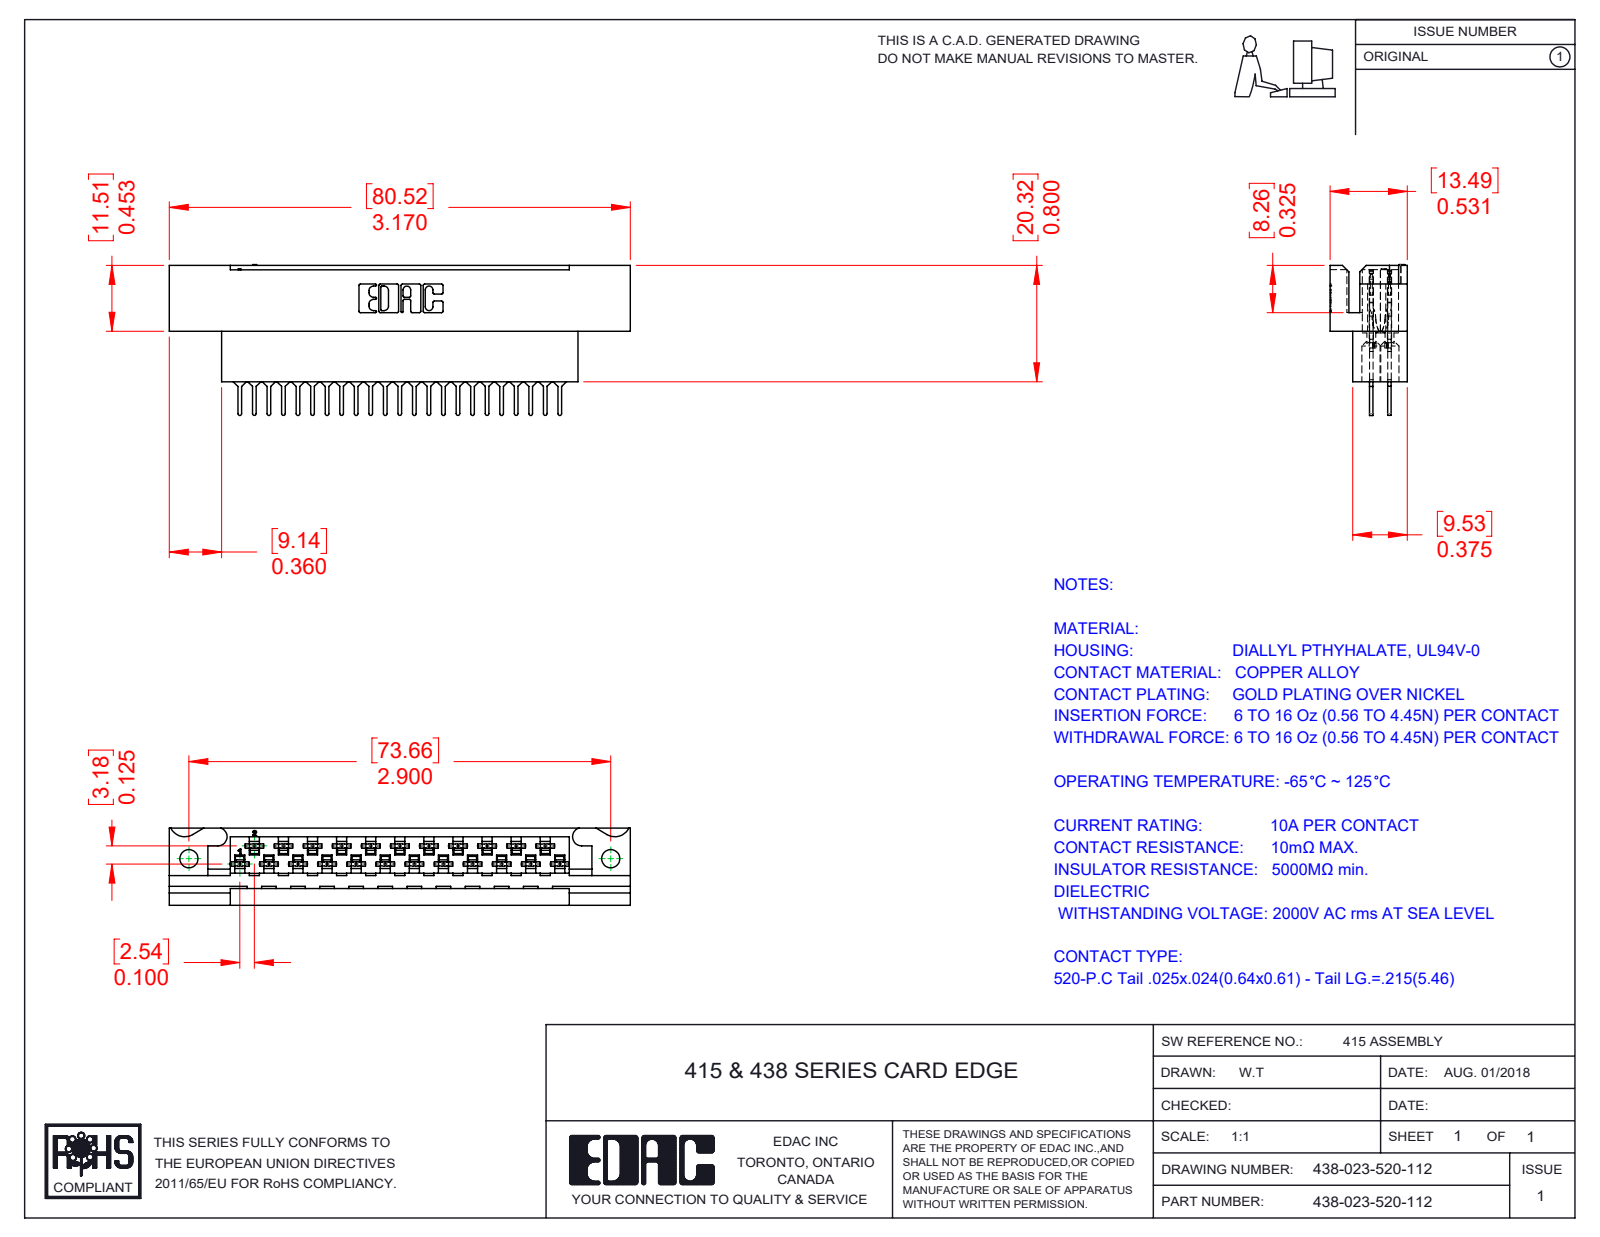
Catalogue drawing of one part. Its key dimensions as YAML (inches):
part_name: "438-210-001_438-210-023-112; 438-023-520-112; 516-290-001_520"
step_written_by: "SolidWorks 2016 (CONFIG_CONTROL_DESIGN)"
units: inches
bodies: {solids: 24, faces: 2410, planar: 1533, cylindrical: 648, other: 229}
overall_size: [3.17, 1.036, 0.531]
volume: 0.787
surface_area: 24.1
round_holes:
  - {diameter: 0.05, count: 23}
  - {diameter: 0.13, count: 23}
  - {diameter: 0.125, count: 1}
  - {diameter: 0.125, count: 1}
partial_cylinders:
  - {radius: 0.012, count: 92}
  - {radius: 0.022, count: 92}
  - {radius: 0.007, count: 46}
  - {radius: 0.008, count: 46}
  - {radius: 0.016, count: 46}
  - {radius: 0.08, count: 46}
  - {radius: 0.013, count: 23}
  - {radius: 0.01, count: 22}
face_to_face_distances: [0.125, 0.074, 0.024, 0.05, 0.531, 0.115, 0.156, 0.295, 0.141, 0.266]
hole_center_spacings: [0.2, 0.4, 0.6, 0.8, 1, 0.1, 0.16, 1.2]
